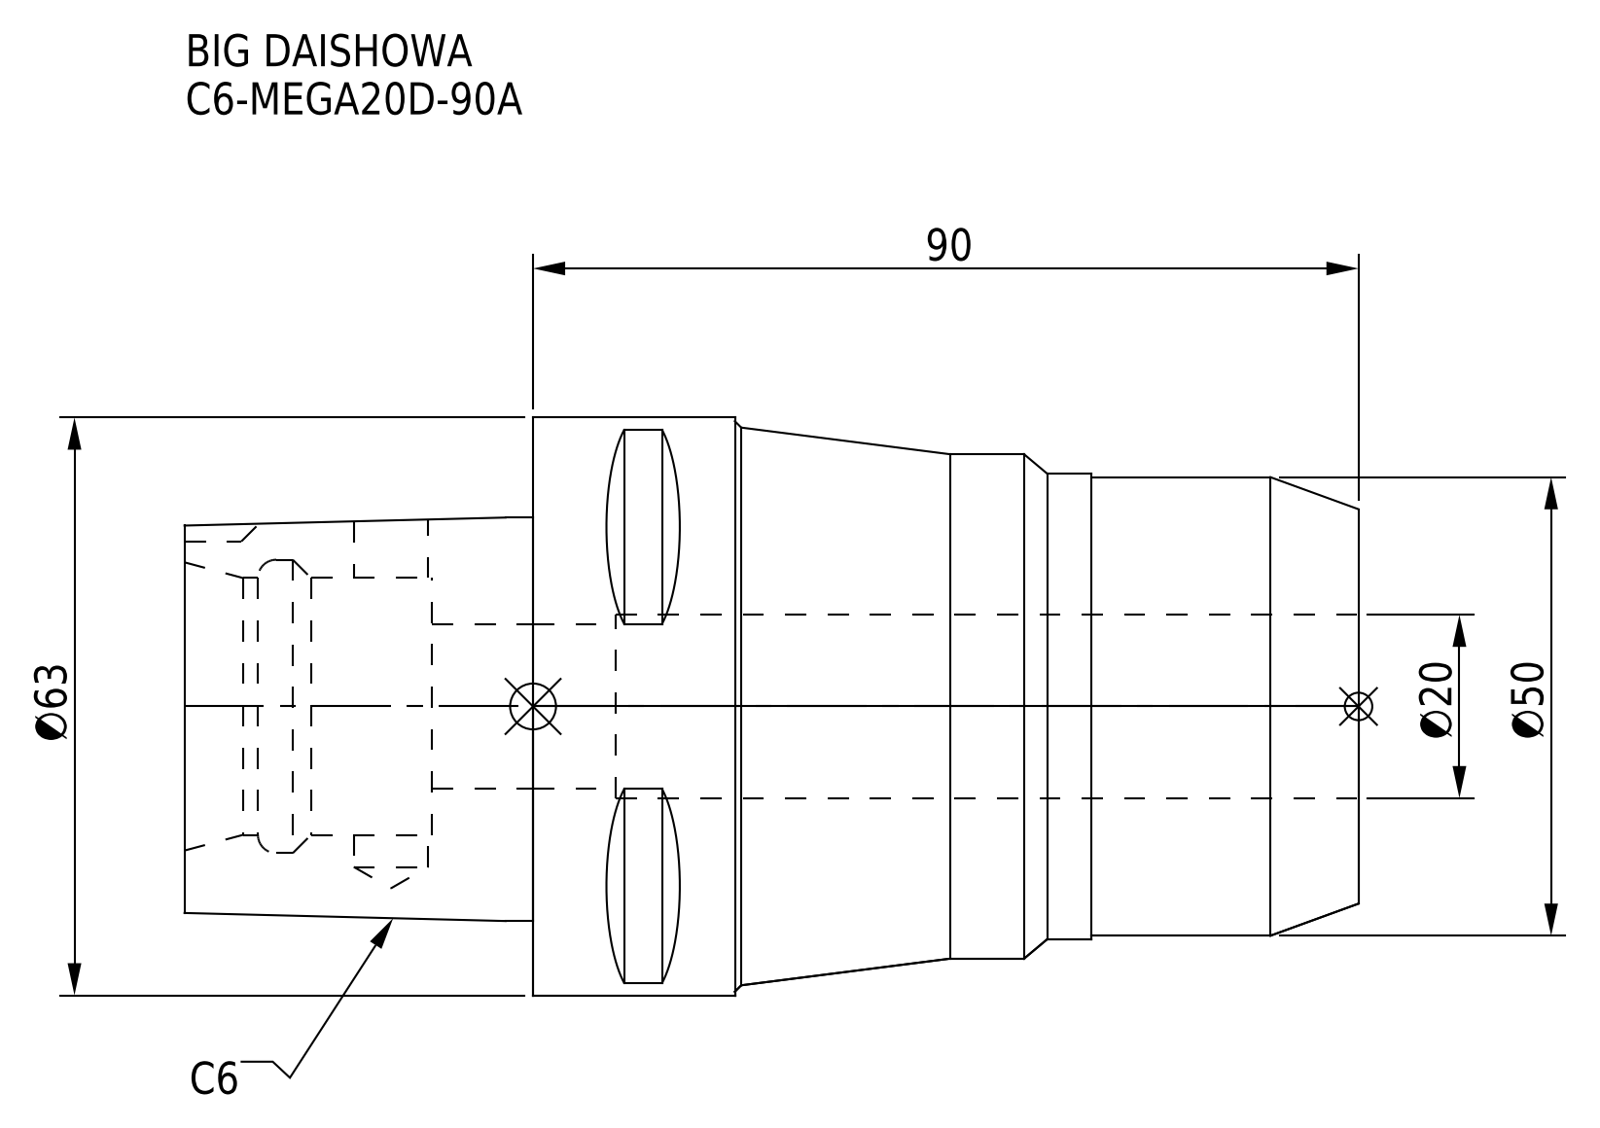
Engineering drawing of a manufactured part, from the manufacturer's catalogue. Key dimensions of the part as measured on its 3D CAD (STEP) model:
Part name (STEP PRODUCT): C6-MEGA20D-90A
STEP written by: CREO PARAMETRIC BY PTC INC, 2016380 (AUTOMOTIVE_DESIGN)
Units: millimetres
Bodies: 1 solid, 70 faces (29 planar, 23 cylindrical, 18 other)
Overall size (bounding box): 128 × 63 × 63
Volume: 224 142 mm³ · Surface area: 34 439 mm²
Round holes (diameter × count): ⌀8.1 ×1, ⌀18 ×1, ⌀20 ×1, ⌀28 ×1, ⌀32 ×1
Round bosses / shafts (diameter × count): ⌀63 ×1, ⌀55 ×1, ⌀50.7 ×1, ⌀50 ×1
Partial cylindrical surfaces — rounded edges, fillets, slot ends (radius × count): R5 ×1
Main face-to-face distances: 90, 128, 38, 101, 11, 27, 24.89, 55.4, 75.95, 14.05
